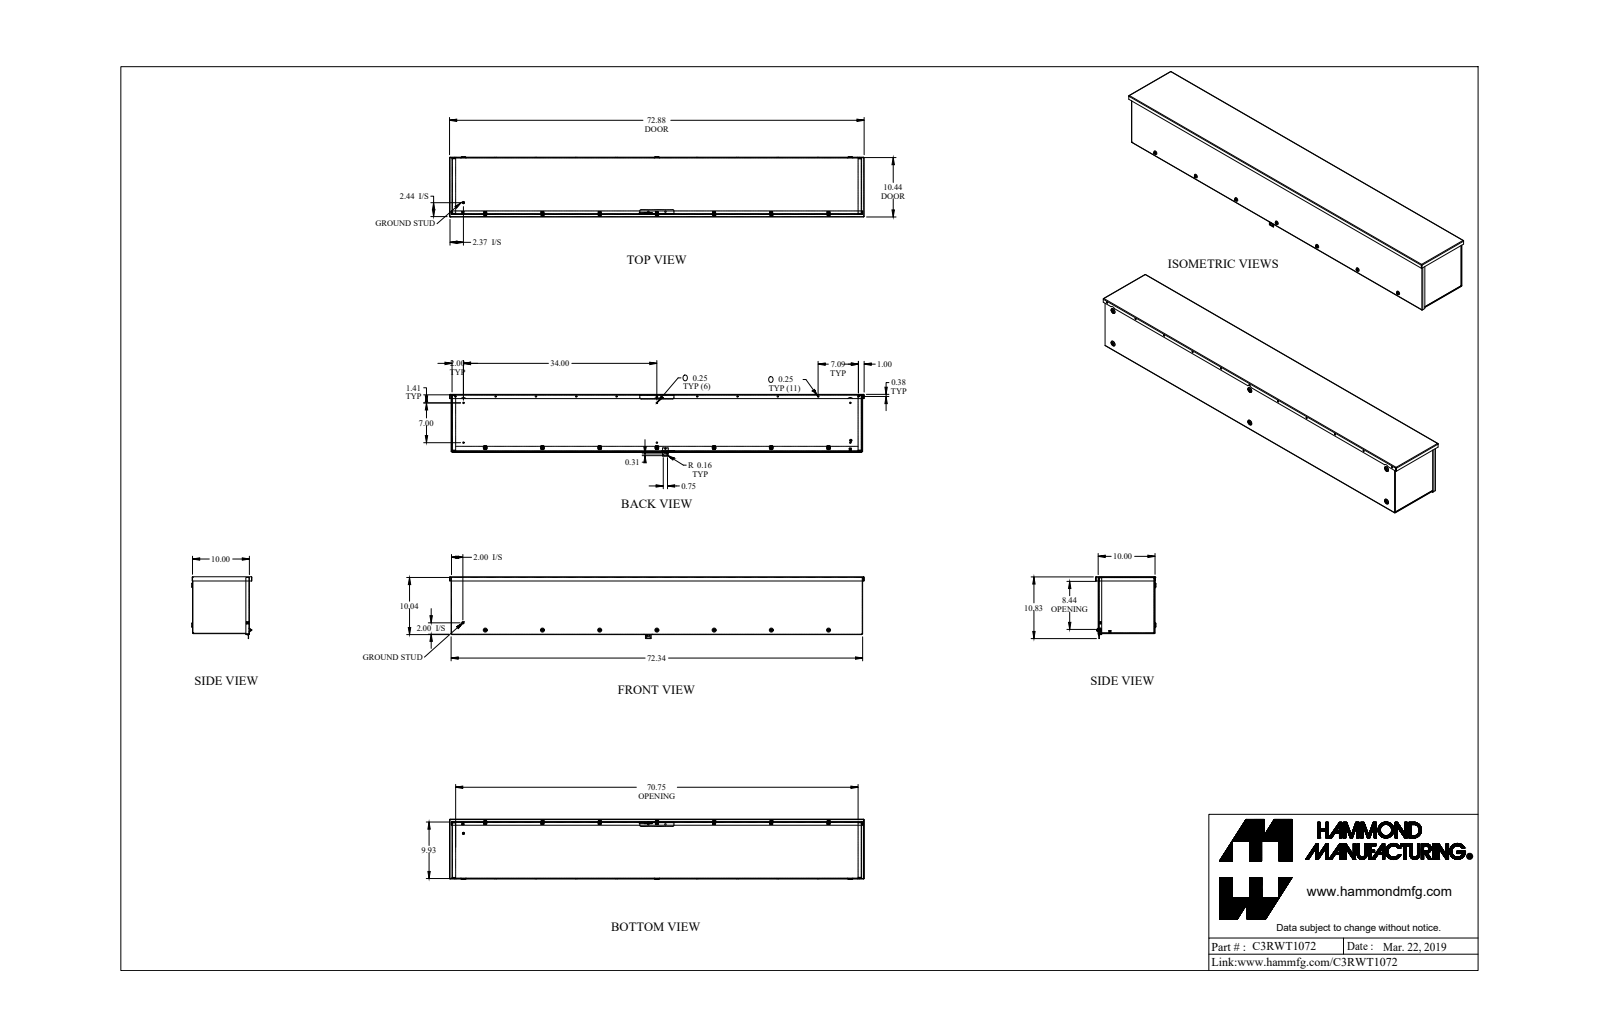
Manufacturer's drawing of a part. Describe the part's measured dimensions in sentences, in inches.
The part is named "C3RWT1072_Default". Its 3-D file was written by "SolidWorks 2019 (CONFIG_CONTROL_DESIGN)". It is 35 solids with 1321 faces: 712 planar, 421 cylindrical and 188 other. Overall it measures 72.875 by 10.871 by 10.594 inches. Its volume is 243.1 cubic inches and its surface area 6 813 square inches. Round holes: 19 of diameter 0.25, 9 of diameter 0.156, 7 of diameter 0.214, 7 of diameter 0.23, 2 of diameter 0.203, 1 of diameter 0.125, 1 of diameter 0.137, 1 of diameter 0.2, 1 of diameter 0.215. Round bosses or shafts: 8 of diameter 0.19, 7 of diameter 0.148, 2 of diameter 0.375, 1 of diameter 0.5, 1 of diameter 0.367, 1 of diameter 0.21, 1 of diameter 0.152, 1 of diameter 0.125. Partial cylindrical surfaces (rounded edges, fillets, slot ends): 28 of radius 0.08, 28 of radius 0.108, 18 of radius 0.036, 18 of radius 0.108, 15 of radius 0.125, 14 of radius 0.022, 7 of radius 0.171, 7 of radius 0.206. The main face-to-face distances are 0.072, 9.928, 10, 0.072, 9.856, 9.856, 9.928, 71.928, 0.144, 72. The hole center spacings are 7.087, 21.263, 28.35, 14.175, 10.057, 14.175, 20.115, 30.172.
